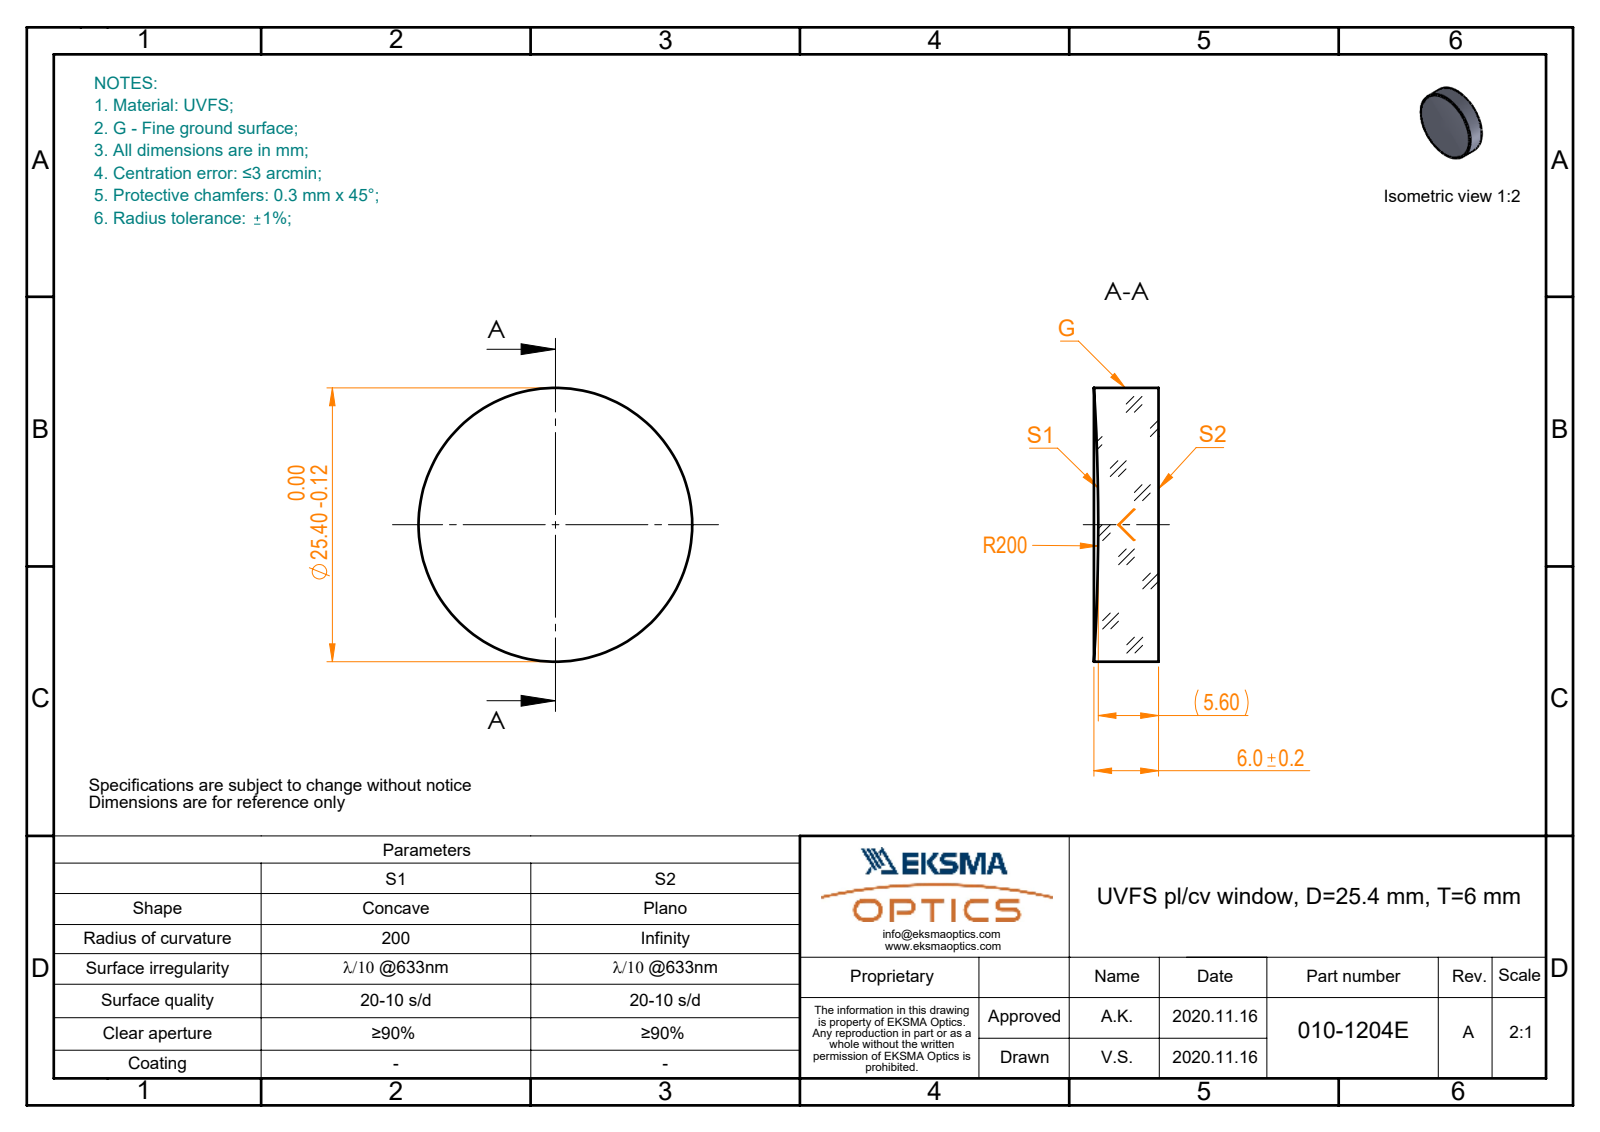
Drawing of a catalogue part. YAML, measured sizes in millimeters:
part_name: "010-1204E_UVFS_PCV_window"
step_written_by: "SolidWorks 2019 (CONFIG_CONTROL_DESIGN)"
units: millimeters
bodies: {solids: 1, faces: 5, planar: 1, cylindrical: 2, other: 2}
overall_size: [25.4, 25.4, 6]
volume: 2938
surface_area: 1493
round_bosses_or_shafts:
  - {diameter: 25.4, count: 1}
